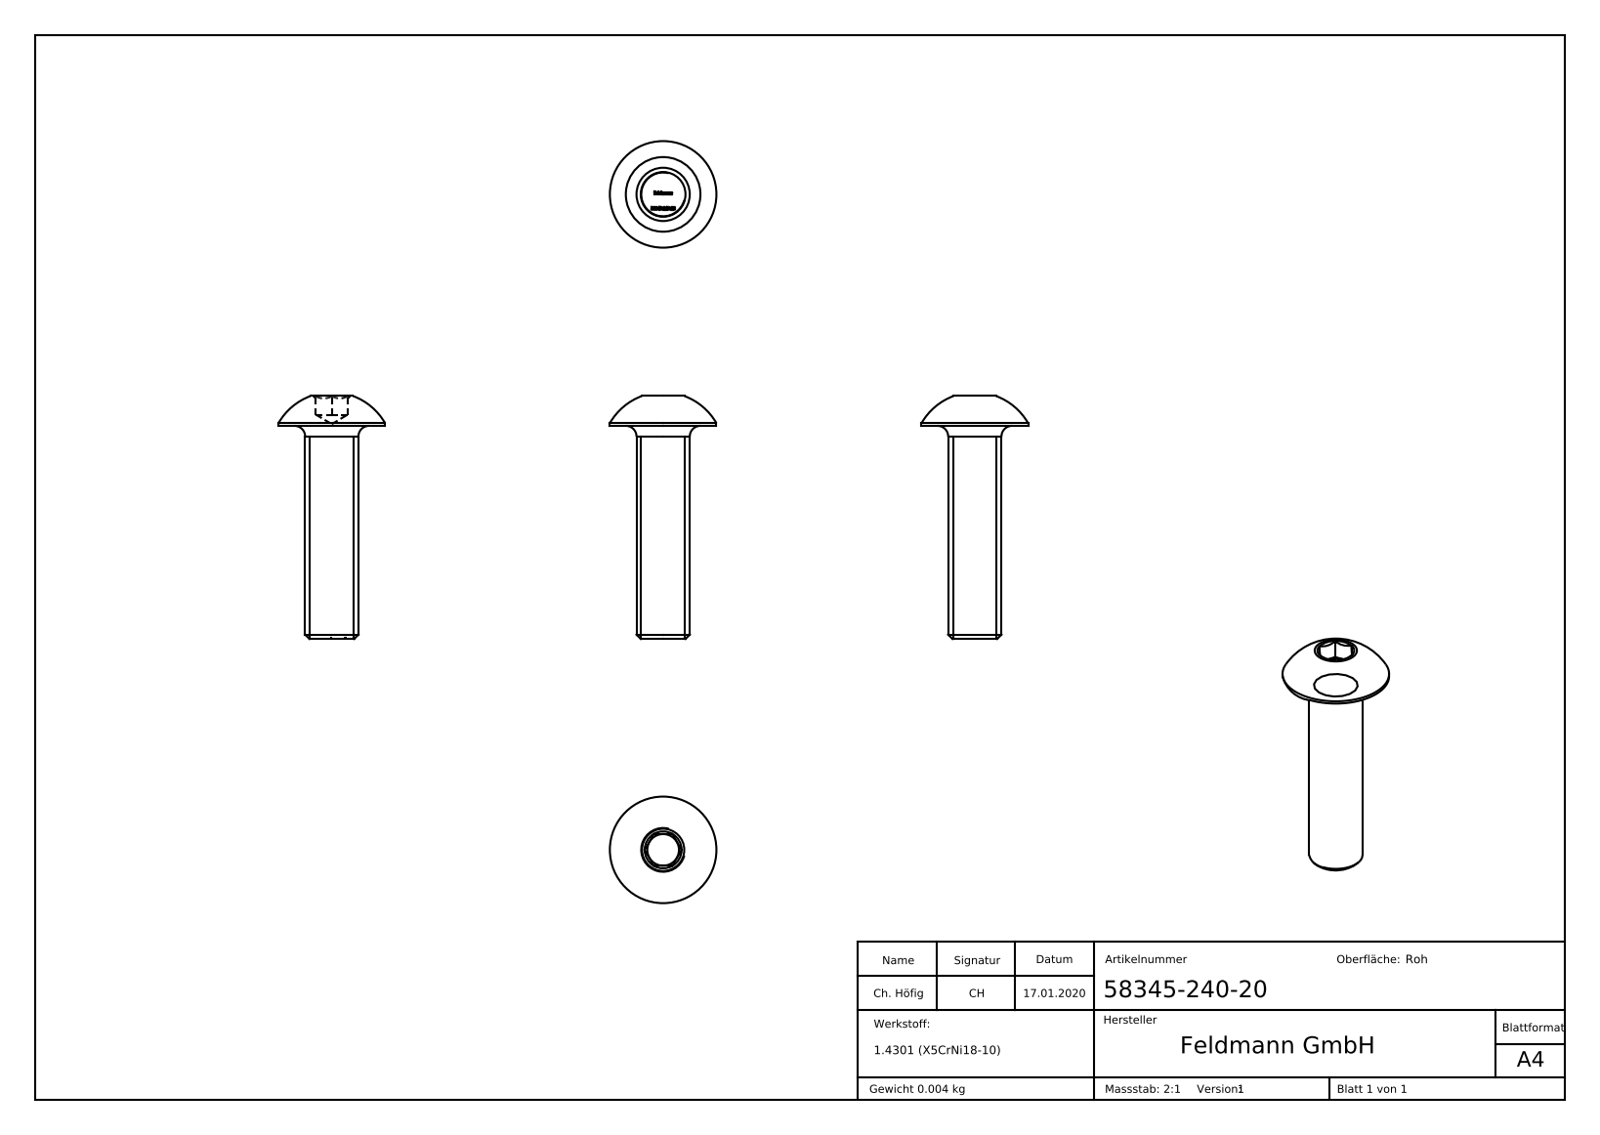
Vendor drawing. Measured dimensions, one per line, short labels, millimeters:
name: 58345-240-20
written by: SolidWorks 2015 (CONFIG_CONTROL_DESIGN)
unit: mm
bodies: 1 solid, 291 faces (154 planar, 2 cylindrical, 135 other)
size: 24.8 × 10 × 10
volume: 523 mm³; area: 516 mm²
bosses: 1× ⌀10, 1× ⌀5
face distances: 20, 3, 2.8, 22.8, 1.05, 1.75, 21.05, 22.7, 20.95, 19.9
